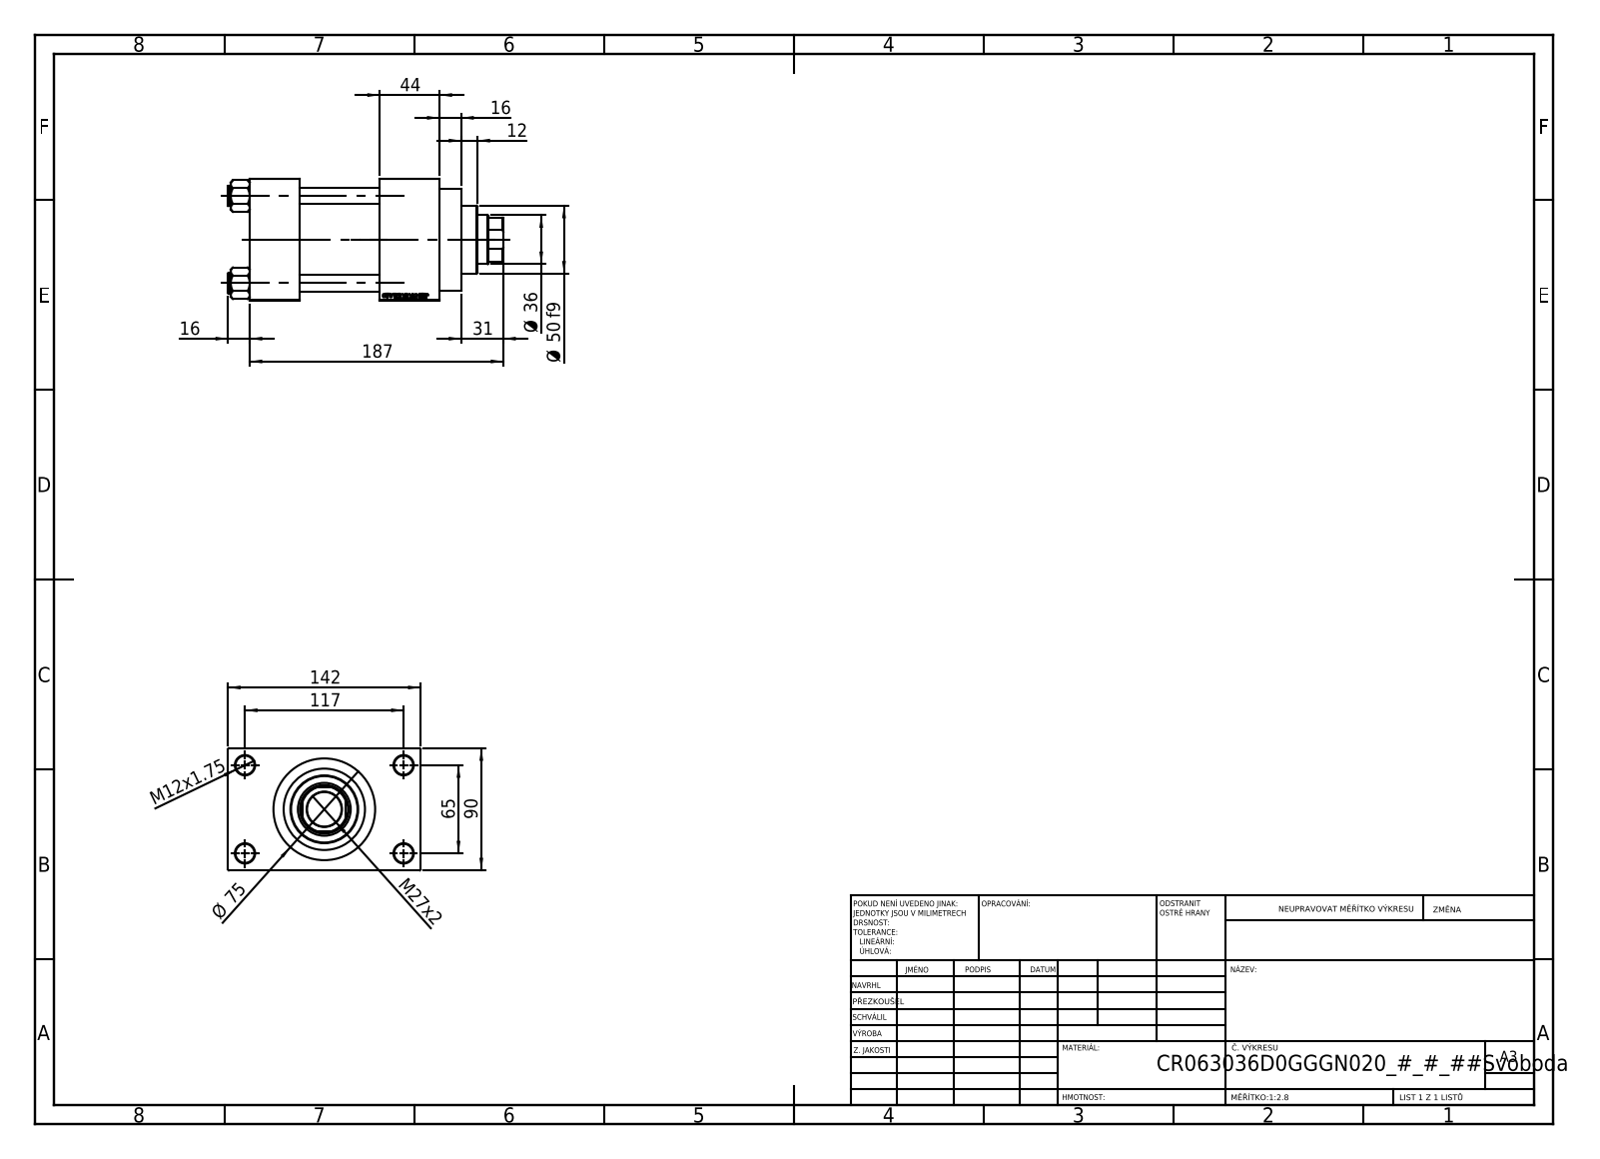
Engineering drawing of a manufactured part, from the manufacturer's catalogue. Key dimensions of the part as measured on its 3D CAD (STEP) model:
Part name (STEP PRODUCT): V215_VC_A; NUT_M5_D; V215CR_D_TYCINKA; V215CR_VCP_D (+1 more)
STEP written by: SolidWorks 2019 (CONFIG_CONTROL_DESIGN)
Units: millimetres
Bodies: 11 solids, 1104 faces (497 planar, 89 cylindrical, 518 other)
Overall size (bounding box): 203 × 142 × 90
Volume: 1 120 000 mm³ · Surface area: 204 077 mm²
Round holes (diameter × count): ⌀12 ×4, ⌀14 ×4, ⌀7 ×2, ⌀20.96 ×2, ⌀30 ×2, ⌀25.5 ×1, ⌀36 ×1, ⌀39 ×1, ⌀50 ×1, ⌀60 ×1, ⌀63 ×1
Round bosses / shafts (diameter × count): ⌀15 ×4, ⌀75 ×1, ⌀69 ×1
Partial cylindrical surfaces — rounded edges, fillets, slot ends (radius × count): R17.5 ×1
Main face-to-face distances: 90, 59, 37, 96, 140, 103, 44, 26, 116, 142
Hole centre spacings: 26.35, 45.47, 64.3, 66.92, 69.81, 90.65, 111.34, 65
